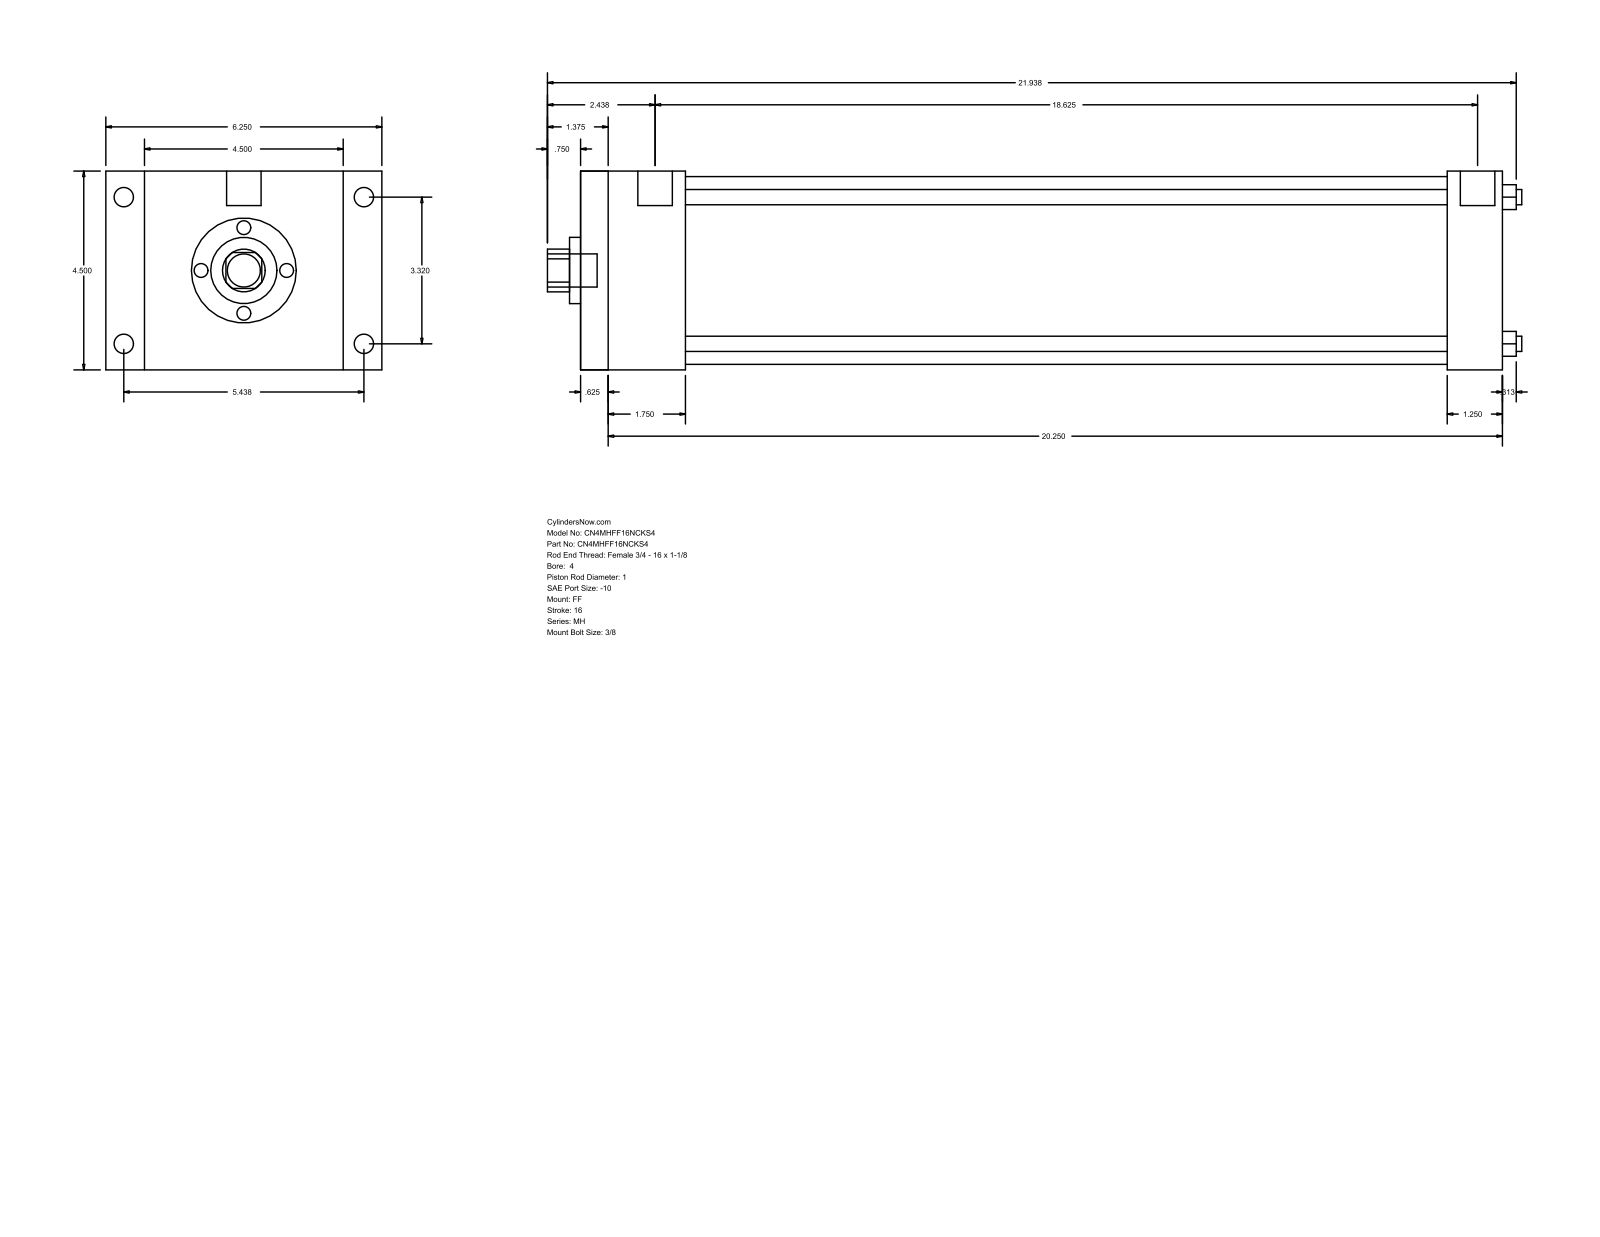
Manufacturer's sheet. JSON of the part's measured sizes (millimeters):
{"part_name": "MH_FF__0400_1", "step_written_by": "GSSL Pune (CONFIG_CONTROL_DESIGN)", "units": "millimeters", "bodies": {"solids": 0, "faces": 92, "planar": 64, "cylindrical": 28, "other": 0}, "overall_size": [560.39, 158.75, 114.3], "round_holes": [[8.76, 4], [25.4, 1], [38.1, 1], [107.95, 1]], "round_bosses_or_shafts": [[11.13, 4], [8.73, 4], [19.84, 2], [19.05, 1]], "partial_cylinders_radius": [[12.29, 1]], "face_to_face_distances": [114.3, 530.22, 15.87, 514.35, 60.33, 44.46, 469.89, 498.47, 482.6, 438.14], "hole_center_spacings": [59.62, 84.32, 119.25]}
